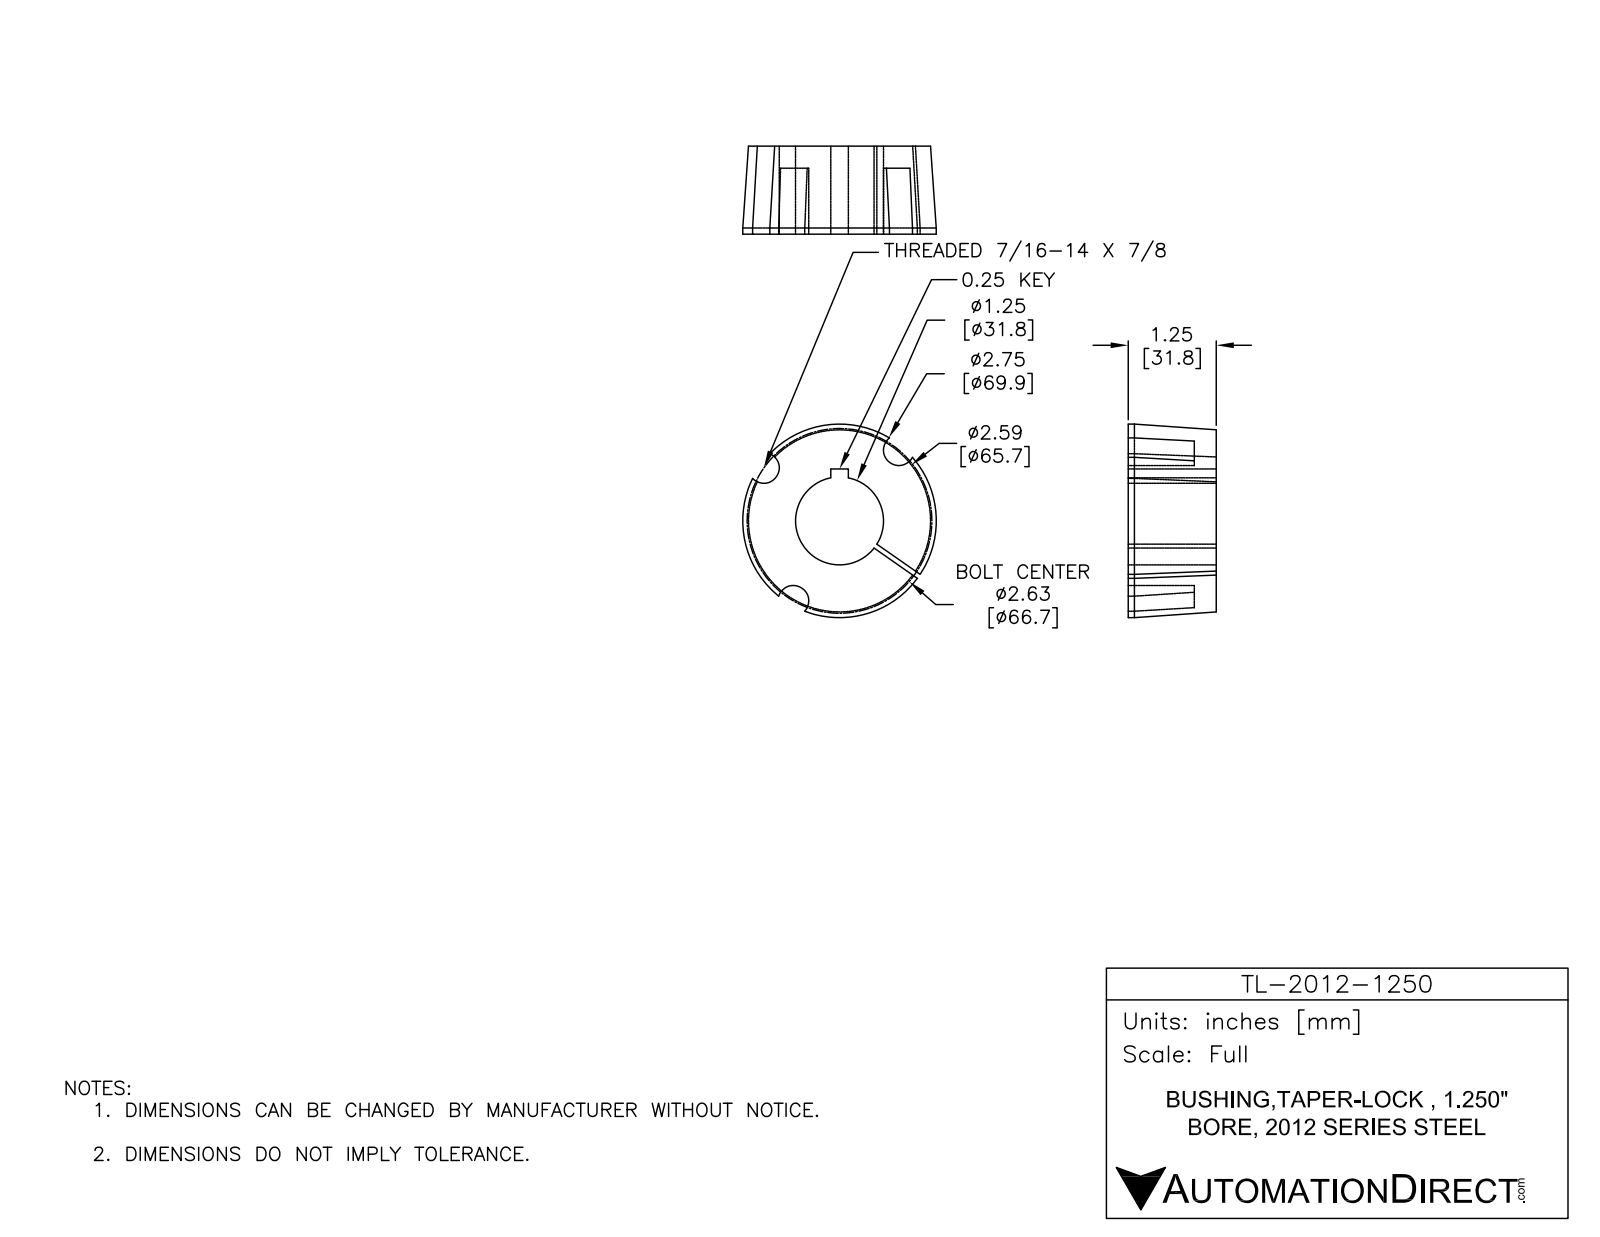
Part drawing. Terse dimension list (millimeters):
name: TL-2012-1250
written by: SolidWorks 2014 (AUTOMOTIVE_DESIGN)
unit: mm
bodies: 1 solid, 25 faces (9 planar, 13 cylindrical, 3 other)
size: 69.9 × 69.9 × 31.8
volume: 83 970 mm³; area: 17 150 mm²
holes: 1× ⌀31.8
bosses: 1× ⌀69.9
rounds: 3× R5.6
face distances: 31.8, 1.8, 6.4, 8, 23.8
